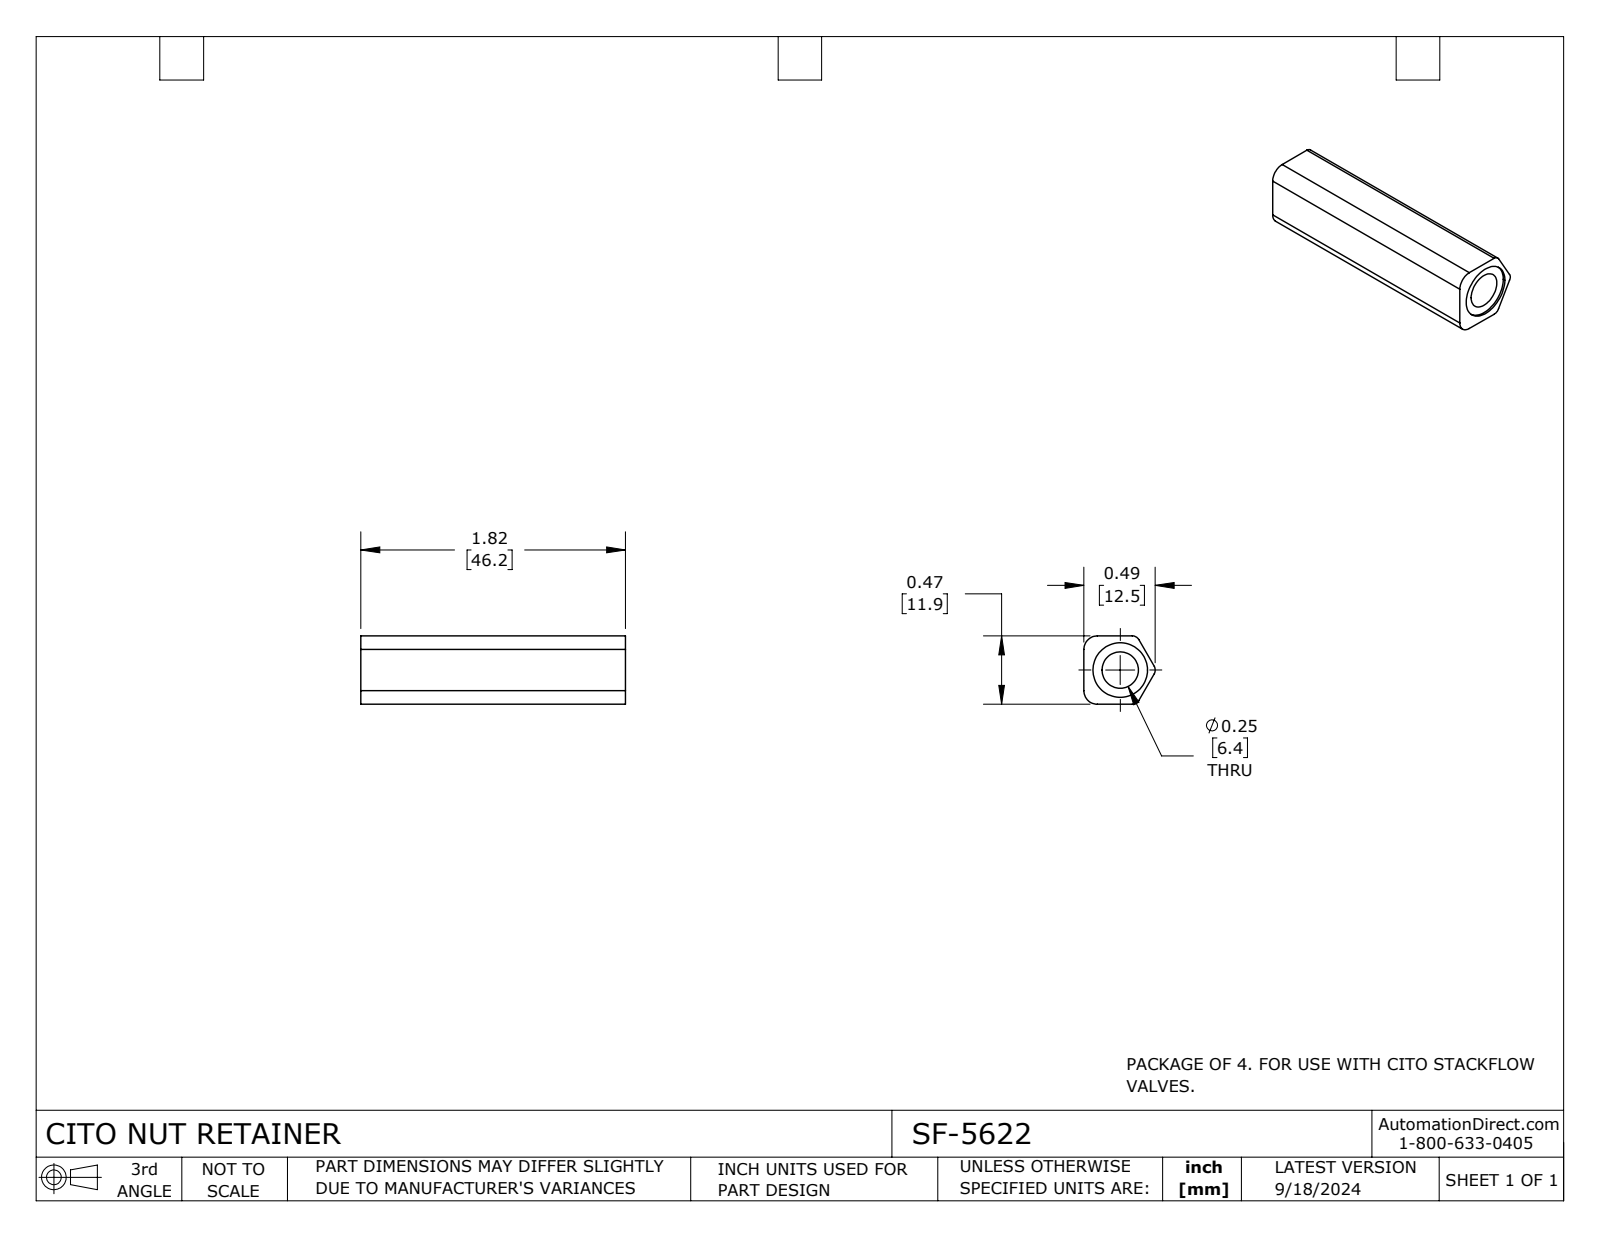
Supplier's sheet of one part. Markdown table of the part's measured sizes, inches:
| quantity | value |
| --- | --- |
| part name | SF-5622 |
| STEP written by | SolidWorks 2023 (CONFIG_CONTROL_DESIGN) |
| units | inches |
| bodies | 1 solid, 20 faces (9 planar, 11 cylindrical, 0 other) |
| overall size | 1.82 × 0.49 × 0.47 |
| volume | 0.269 in³ |
| surface area | 4.728 in² |
| round holes (diameter × count) | 0.25 × 1, 0.375 × 1 |
| partial cylindrical surfaces (radius × count) | 0.05 × 3, 0.093 × 2 |
| main face-to-face distances | 0.47, 0.015, 1.805, 1.82, 1.79 |
